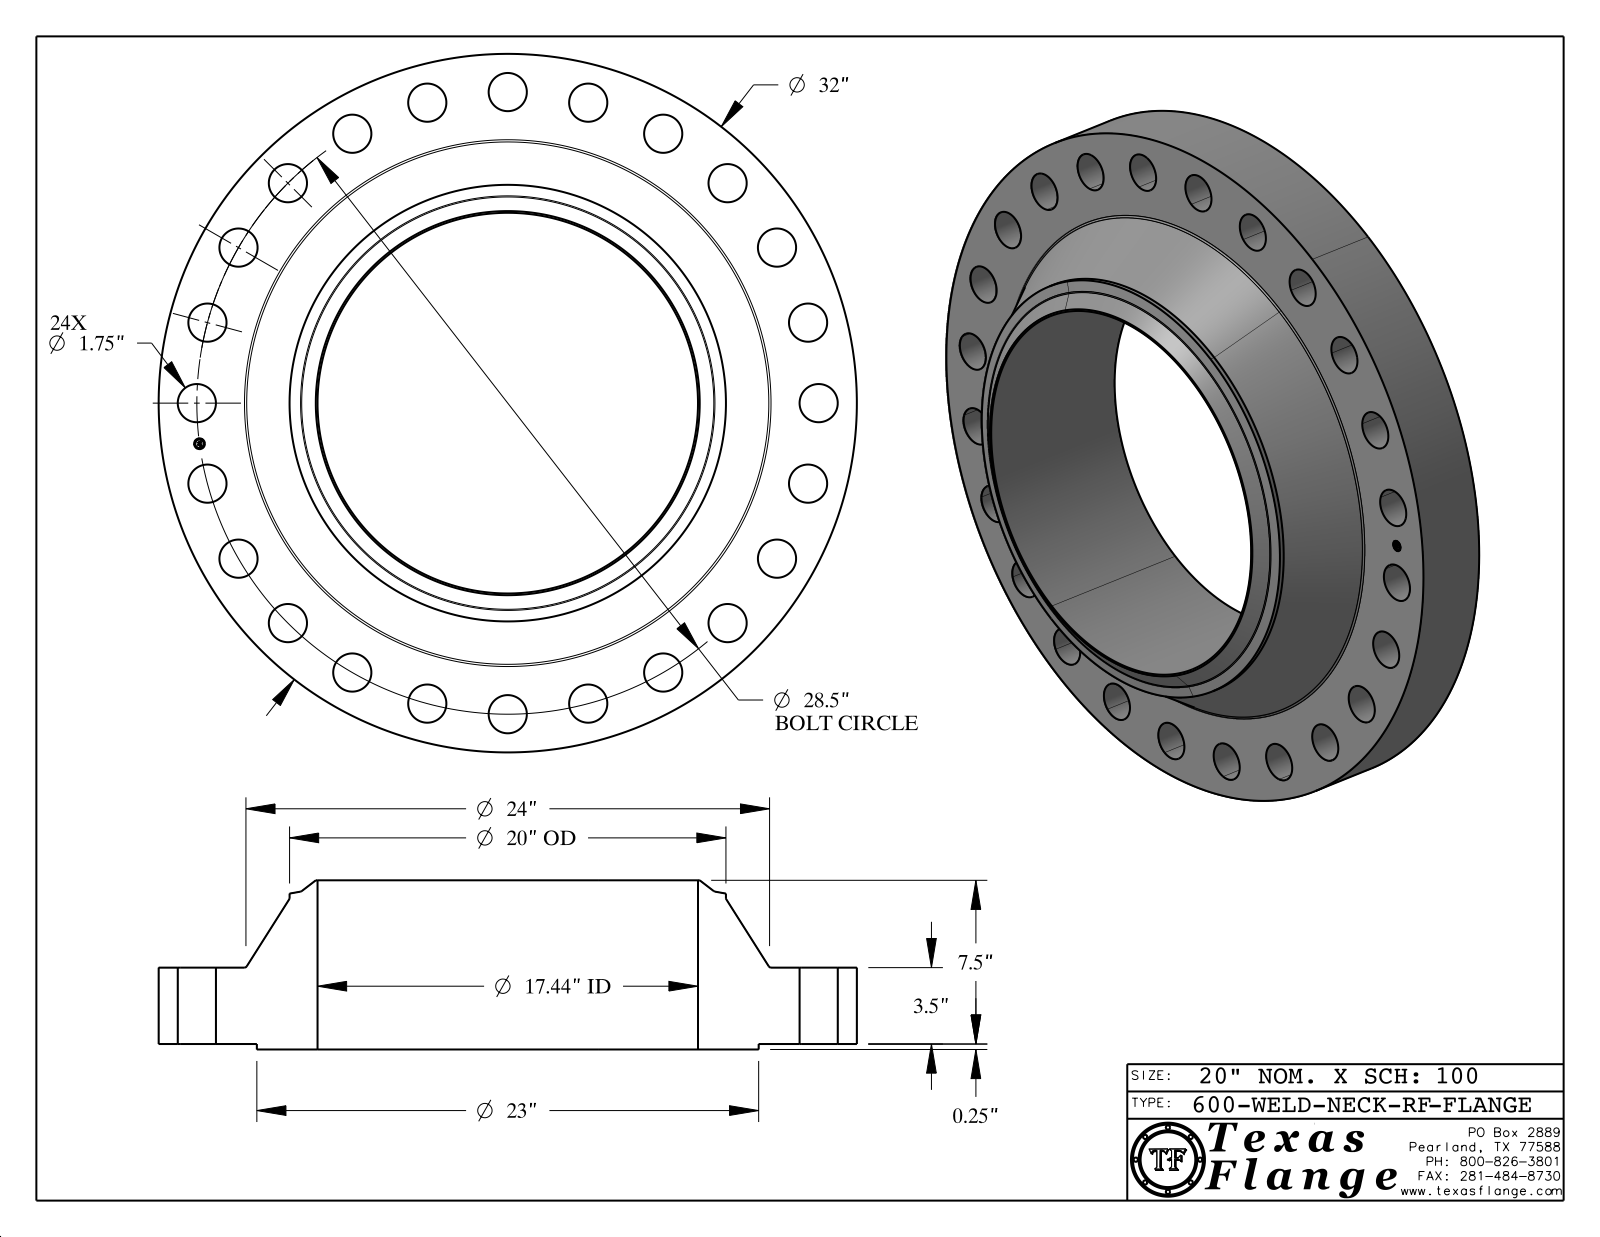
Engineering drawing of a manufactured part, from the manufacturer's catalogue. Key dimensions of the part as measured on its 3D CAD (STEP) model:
Part name (STEP PRODUCT): 600-WELD-NECK-RF
STEP written by: CATIA V5 STEP AP214 (AUTOMOTIVE_DESIGN)
Units: inches
Bodies: 1 solid, 455 faces (369 planar, 76 cylindrical, 10 other)
Overall size (bounding box): 32 × 32 × 7.75
Volume: 2 306 in³ · Surface area: 2 416 in²
Round holes (diameter × count): ⌀1.75 ×24, ⌀0.495 ×1, ⌀17.438 ×1
Round bosses / shafts (diameter × count): ⌀0.03 ×8, ⌀32 ×1, ⌀23 ×1, ⌀20 ×1, ⌀0.39 ×1
Main face-to-face distances: 3.5, 0.25, 3.75, 7.75, 7.5, 4, 0.015, 3.735, 3.485, 4.015
Hole centre spacings: 14.25, 3.72, 7.376, 24.682, 26.331, 27.529, 20.153, 10.907
